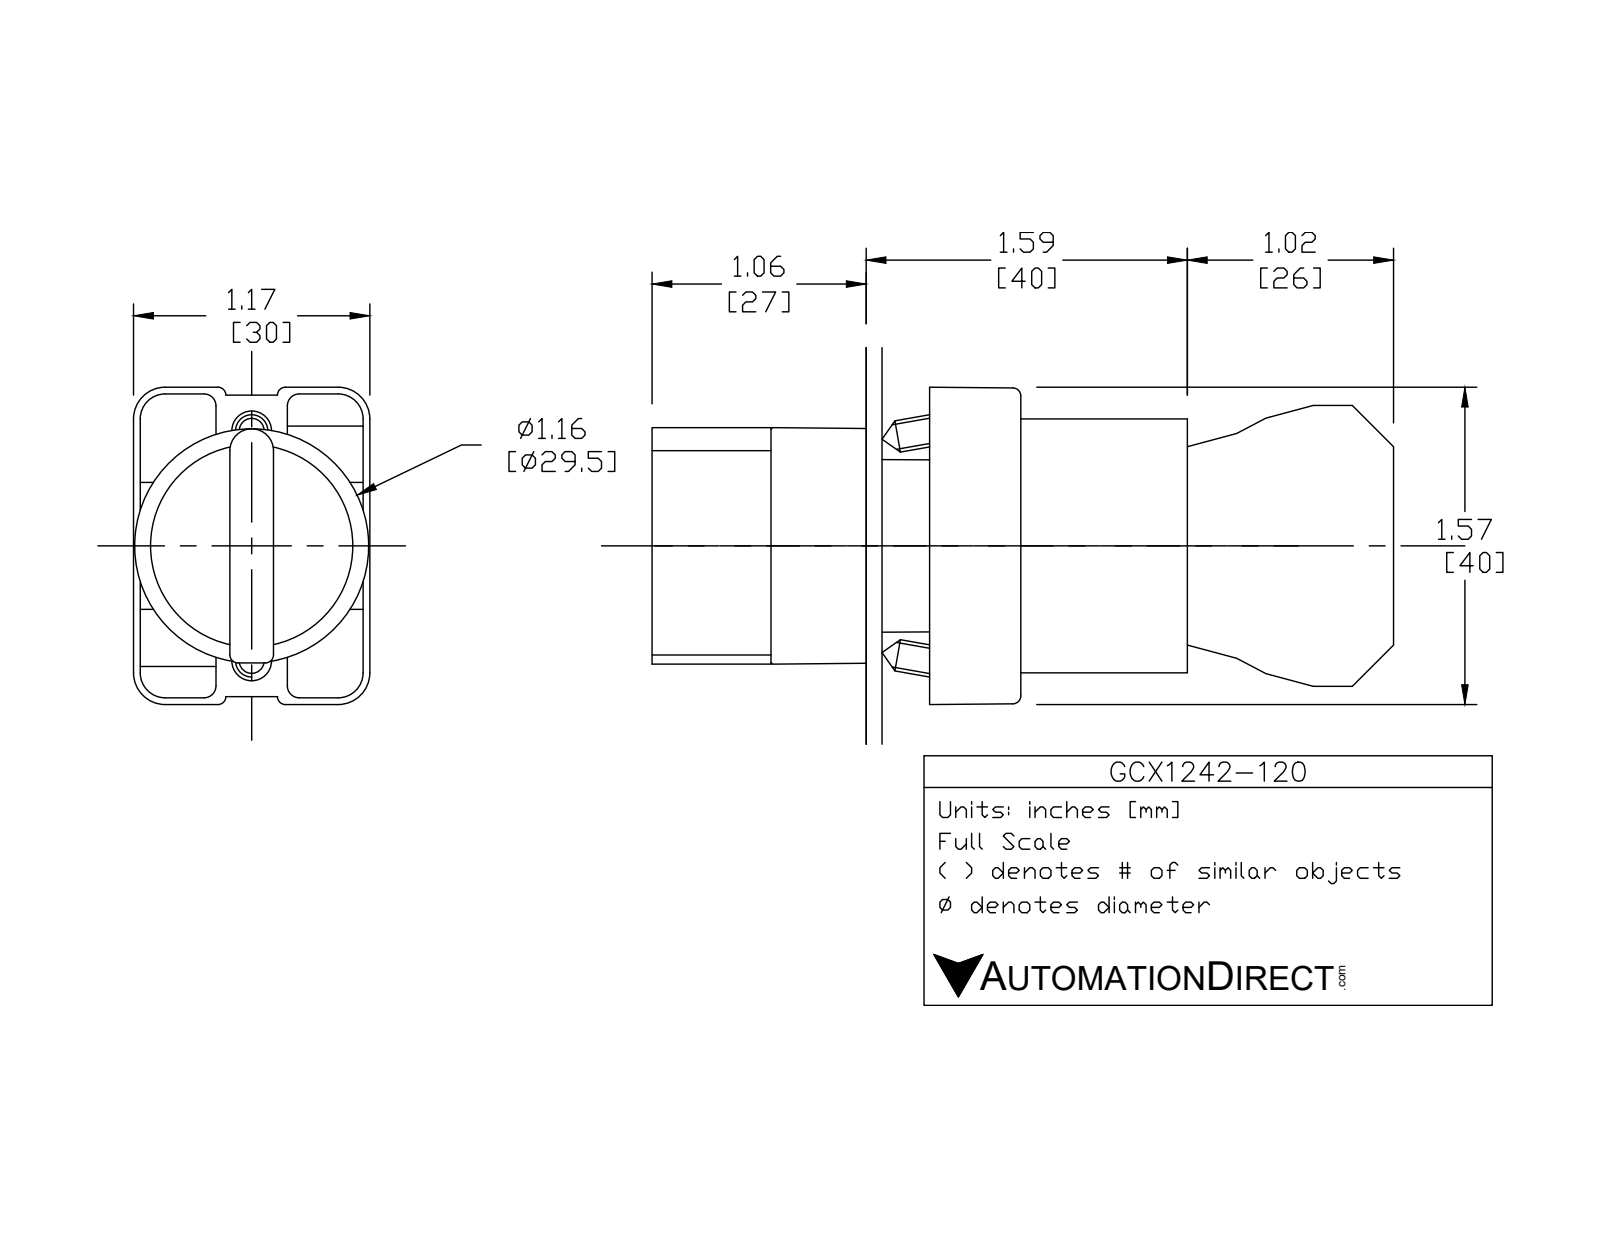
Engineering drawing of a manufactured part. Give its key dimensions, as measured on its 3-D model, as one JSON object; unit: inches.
{"part_name": "ECX1050; ecx1040; ecx1029; GCX1242-120 (+1 more)", "step_written_by": "SolidWorks 2016 (AUTOMOTIVE_DESIGN)", "units": "inches", "bodies": {"solids": 8, "faces": 445, "planar": 263, "cylindrical": 151, "other": 31}, "overall_size": [3.653, 1.581, 1.177], "volume_in3": 2.799, "surface_area_in2": 39, "round_holes": [[0.079, 2], [0.124, 2], [0.13, 2], [0.087, 1], [0.197, 1], [0.469, 1], [0.878, 1], [0.888, 1], [1.024, 1]], "round_bosses_or_shafts": [[0.157, 4], [1.175, 1], [1.004, 1], [0.945, 1], [0.856, 1], [0.78, 1], [0.504, 1]], "partial_cylinders_radius": [[0.059, 24], [0.041, 12], [0.124, 12], [0.157, 12], [0.039, 9], [0.128, 2], [0.02, 1], [0.063, 1]], "face_to_face_distances": [0.827, 2.02, 1.193, 0.579, 1.244, 1.171, 0.472, 0.469, 0.031, 0.033], "hole_center_spacings": [0.236, 0.544, 0.472, 0.49]}
